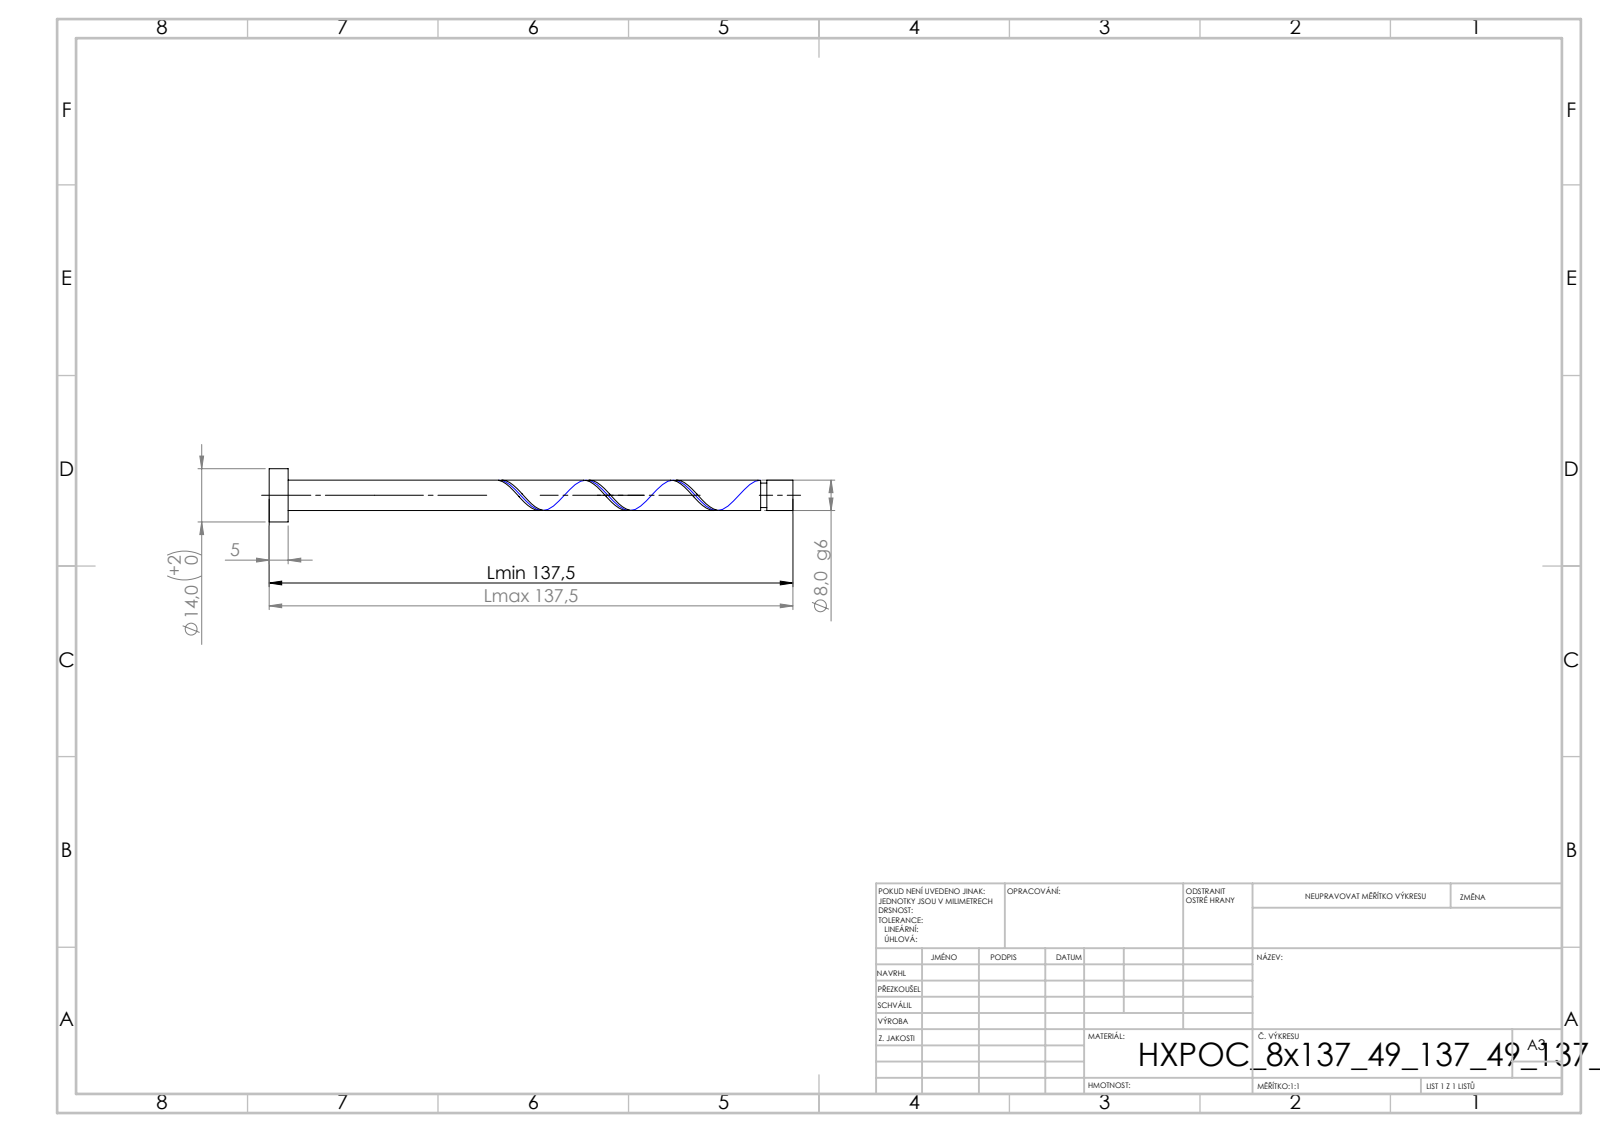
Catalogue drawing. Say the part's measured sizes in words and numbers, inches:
Its 3-D file was written by "SolidWorks 2019 (CONFIG_CONTROL_DESIGN)". It is 1 solid with 21 faces: 6 planar, 14 cylindrical and 1 other. Overall it measures 5.413 by 0.551 by 0.551 inches. Its volume is 0.448 cubic inches and its surface area 6.163 square inches. Round bosses or shafts: 1 of diameter 0.551, 1 of diameter 0.315, 1 of diameter 0.252. The main face-to-face distances are 0.197, 5.413, 5.216, 5.143, 4.946, 0.27, 5.08, 4.883, 0.063, 0.333.
